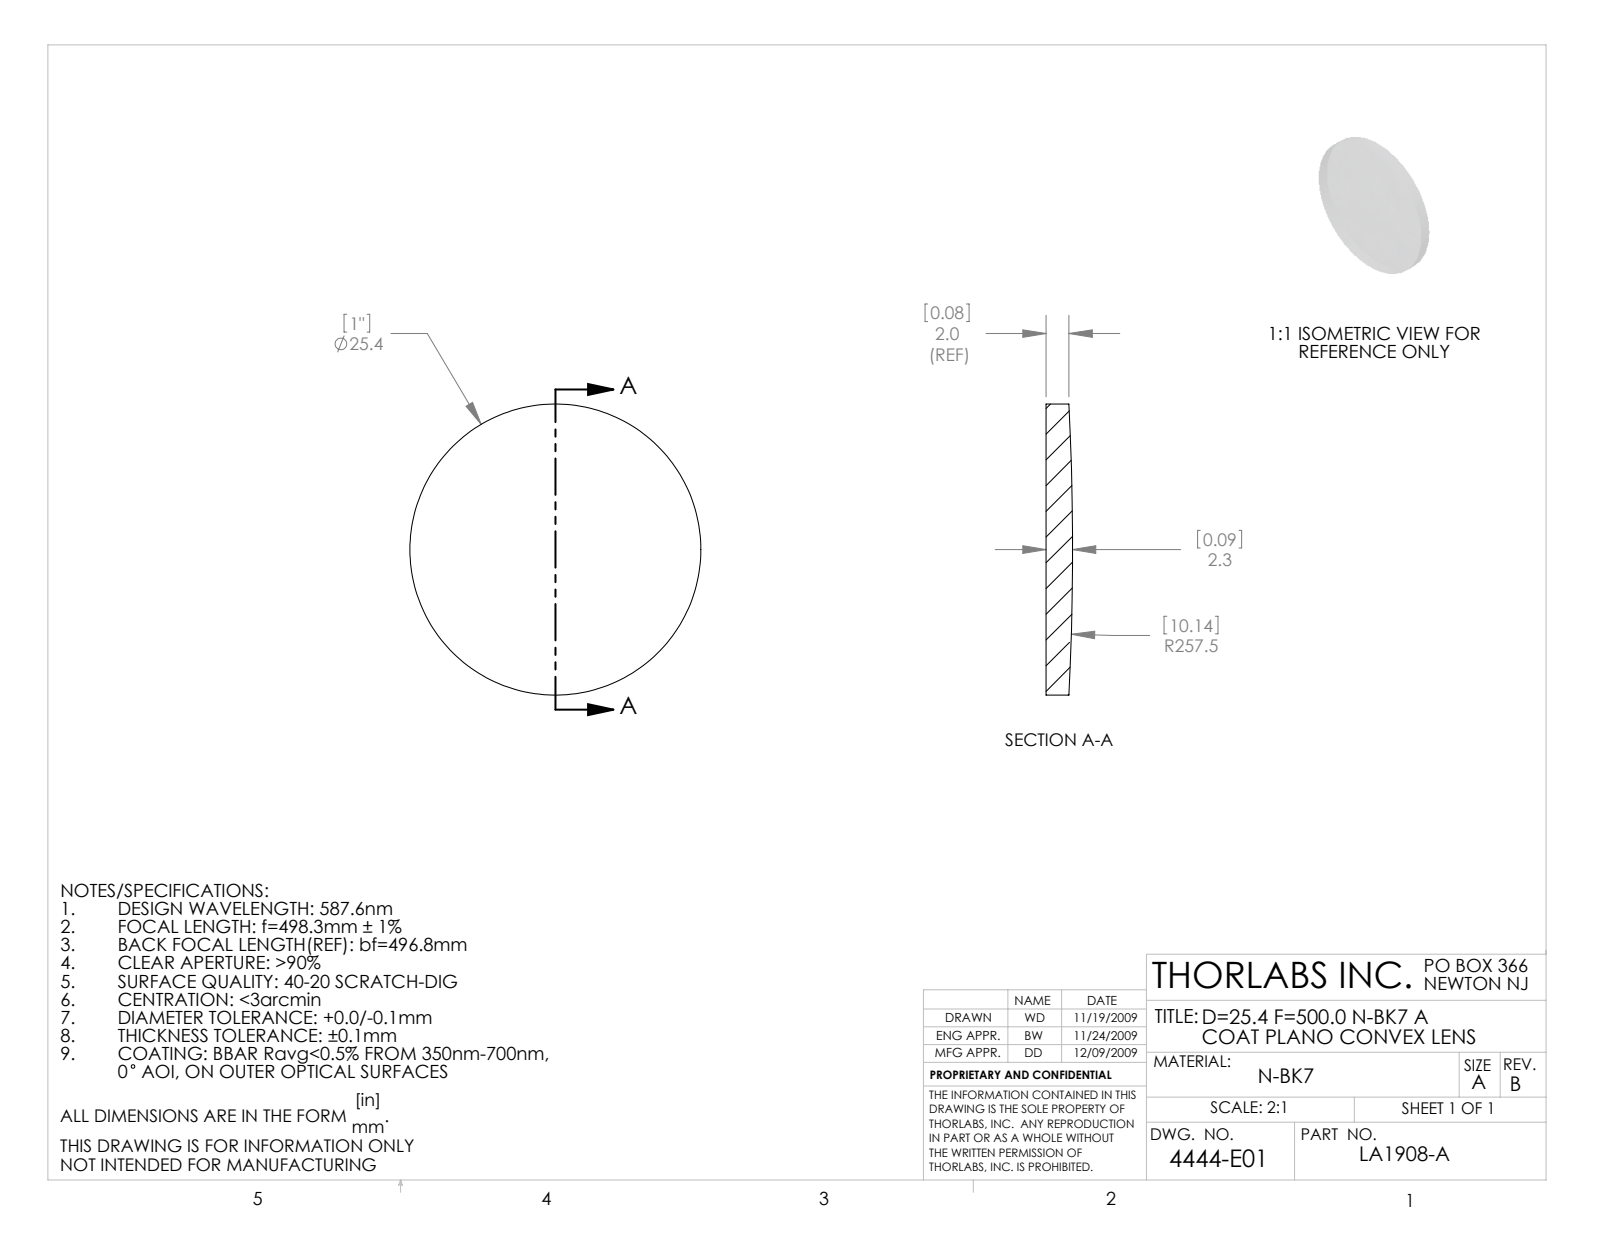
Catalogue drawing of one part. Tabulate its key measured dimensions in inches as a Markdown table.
| quantity | value |
| --- | --- |
| part name | 4444-E0W |
| STEP written by | SolidWorks 2009 (AUTOMOTIVE_DESIGN) |
| units | inches |
| bodies | 1 solid, 5 faces (1 planar, 2 cylindrical, 2 other) |
| overall size | 1 × 1 × 0.091 |
| volume | 0.067 in³ |
| surface area | 1.818 in² |
| round bosses / shafts (diameter × count) | 1 × 1 |
